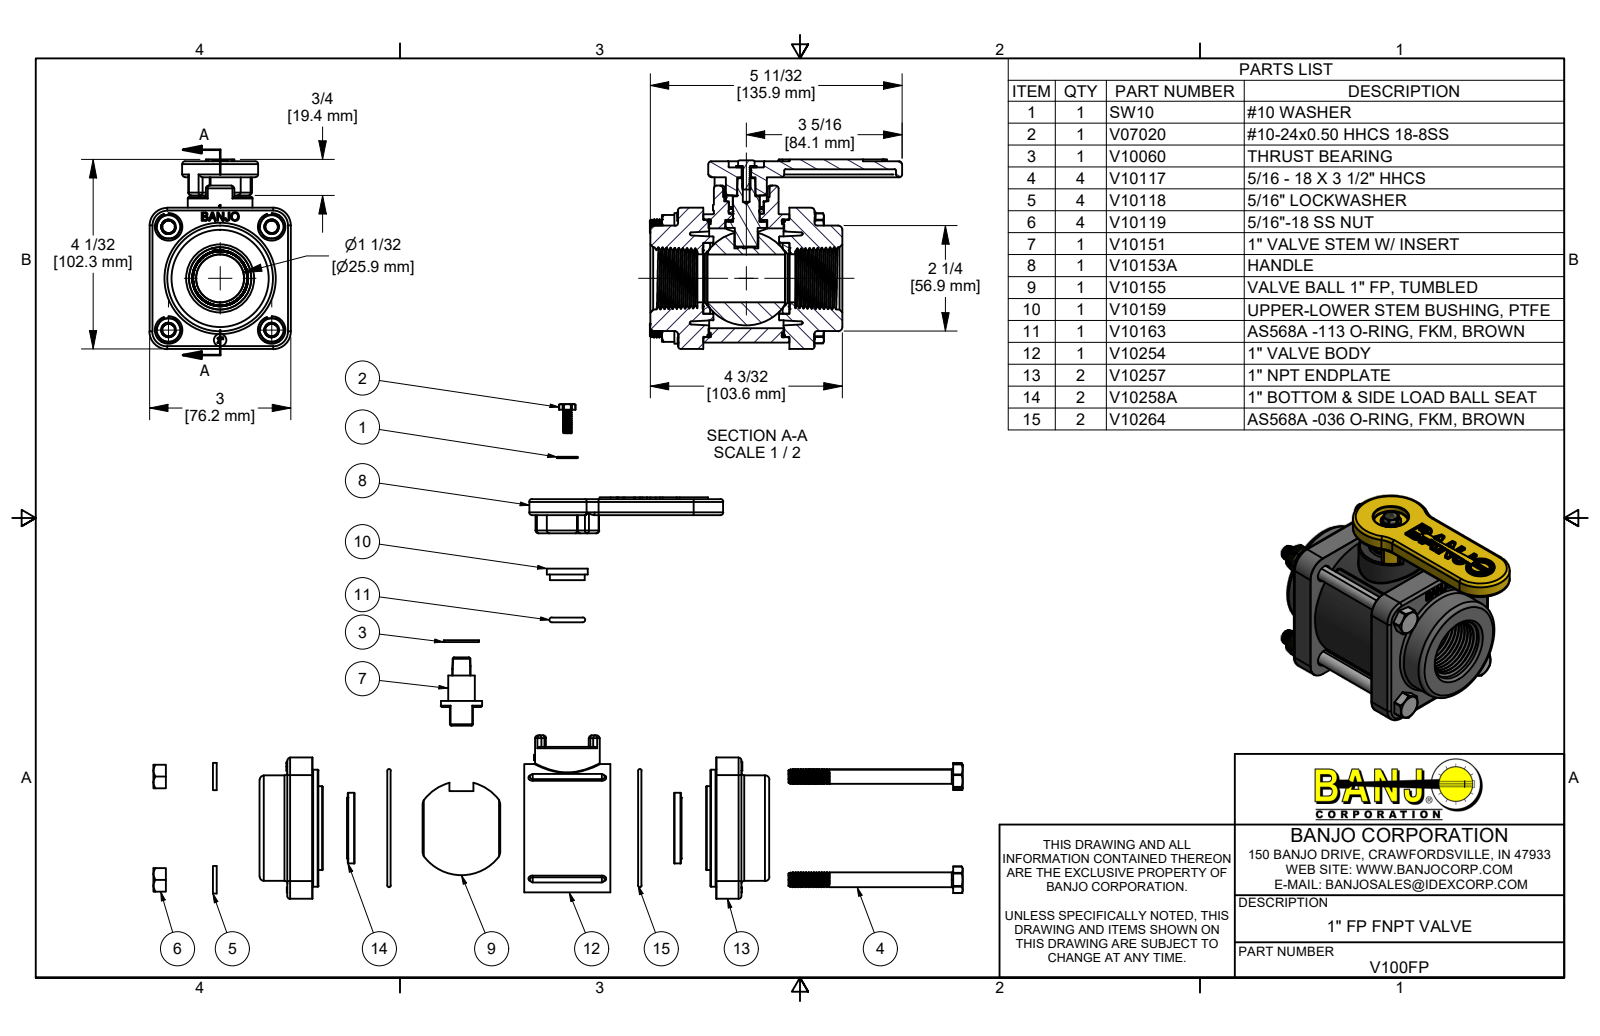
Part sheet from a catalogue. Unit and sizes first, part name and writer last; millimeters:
Units: millimetres
Overall size (bounding box): 136.3 × 102 × 76.2
Round holes (diameter × count): ⌀6.4 ×4, ⌀8.2 ×4, ⌀9.3 ×4, ⌀2.3 ×1, ⌀3.7 ×1, ⌀5.1 ×1, ⌀5.2 ×1, ⌀6.6 ×1, ⌀9.6 ×1, ⌀13.5 ×1, ⌀14.3 ×1, ⌀14.5 ×1
Round bosses / shafts (diameter × count): ⌀6.8 ×60, ⌀14.8 ×4, ⌀8 ×4, ⌀69.2 ×1, ⌀63 ×1, ⌀58.5 ×1, ⌀56.9 ×1, ⌀45.2 ×1
Partial cylindrical surfaces — rounded edges, fillets, slot ends (radius × count): R1.5 ×58, R0.8 ×32, R0.8 ×12, R3.4 ×8, R0.4 ×4, R2 ×4, R7.2 ×4, R9.5 ×4
Main face-to-face distances: 3.2, 44.1, 76.2, 31.8, 74.4, 13.6, 60.8, 47.2, 60.8, 13.6
Hole centre spacings: 39.4, 55.7, 28.4, 67.2, 78.7, 9.2, 33.3, 65.3
Volume: 361 700 mm³ · Surface area: 126 900 mm²
Bodies: 27 solids, 2068 faces (715 planar, 621 cylindrical, 732 other)
Part name (STEP PRODUCT): V100FP; V10117; V10254; V10118 (+8 more)
STEP written by: Autodesk Inventor 2022 (AUTOMOTIVE_DESIGN)
